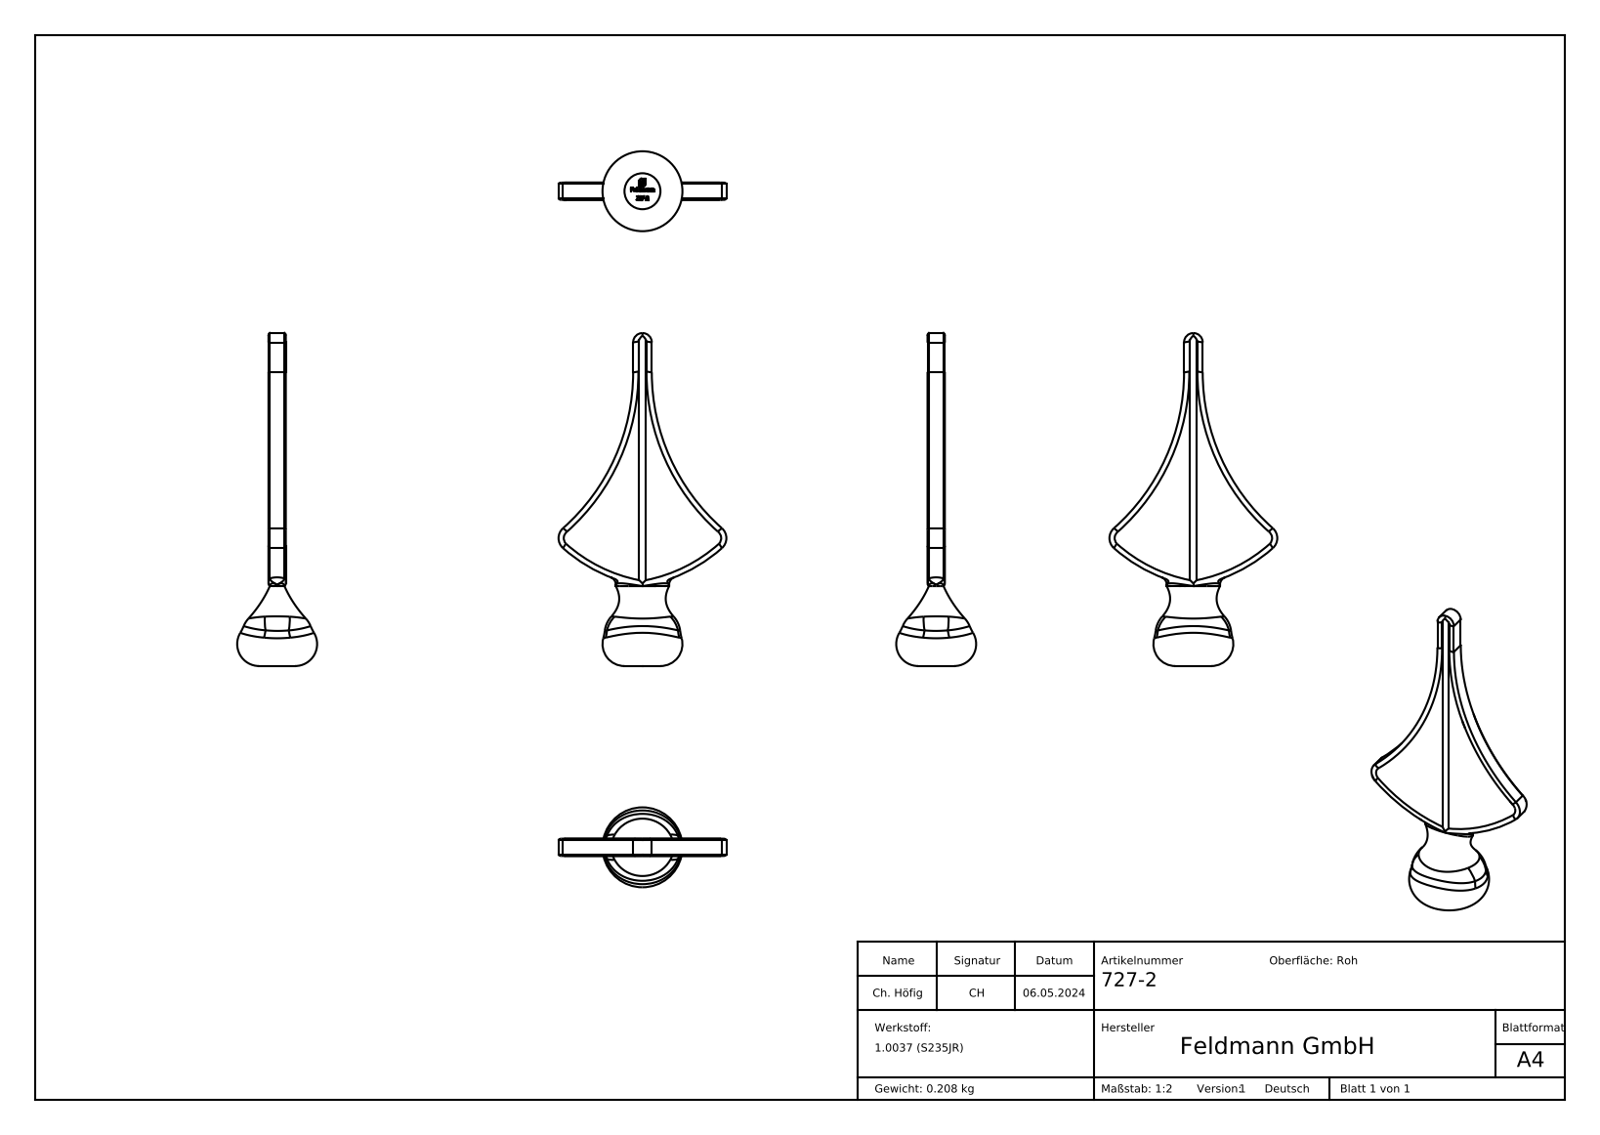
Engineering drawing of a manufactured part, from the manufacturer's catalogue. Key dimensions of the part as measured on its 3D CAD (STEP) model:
Part name (STEP PRODUCT): 727-2
STEP written by: SolidWorks 2018 (CONFIG_CONTROL_DESIGN)
Units: millimetres
Bodies: 1 solid, 251 faces (128 planar, 9 cylindrical, 114 other)
Overall size (bounding box): 125 × 63 × 30
Volume: 26 723 mm³ · Surface area: 9 156 mm²
Partial cylindrical surfaces — rounded edges, fillets, slot ends (radius × count): R1.81 ×2, R5 ×2, R60 ×2, R78.13 ×2, R3.5 ×1
Main face-to-face distances: 5.5, 7, 1.93, 2.75, 4.39, 0.32, 1.81, 3.21, 4.45, 3.66
